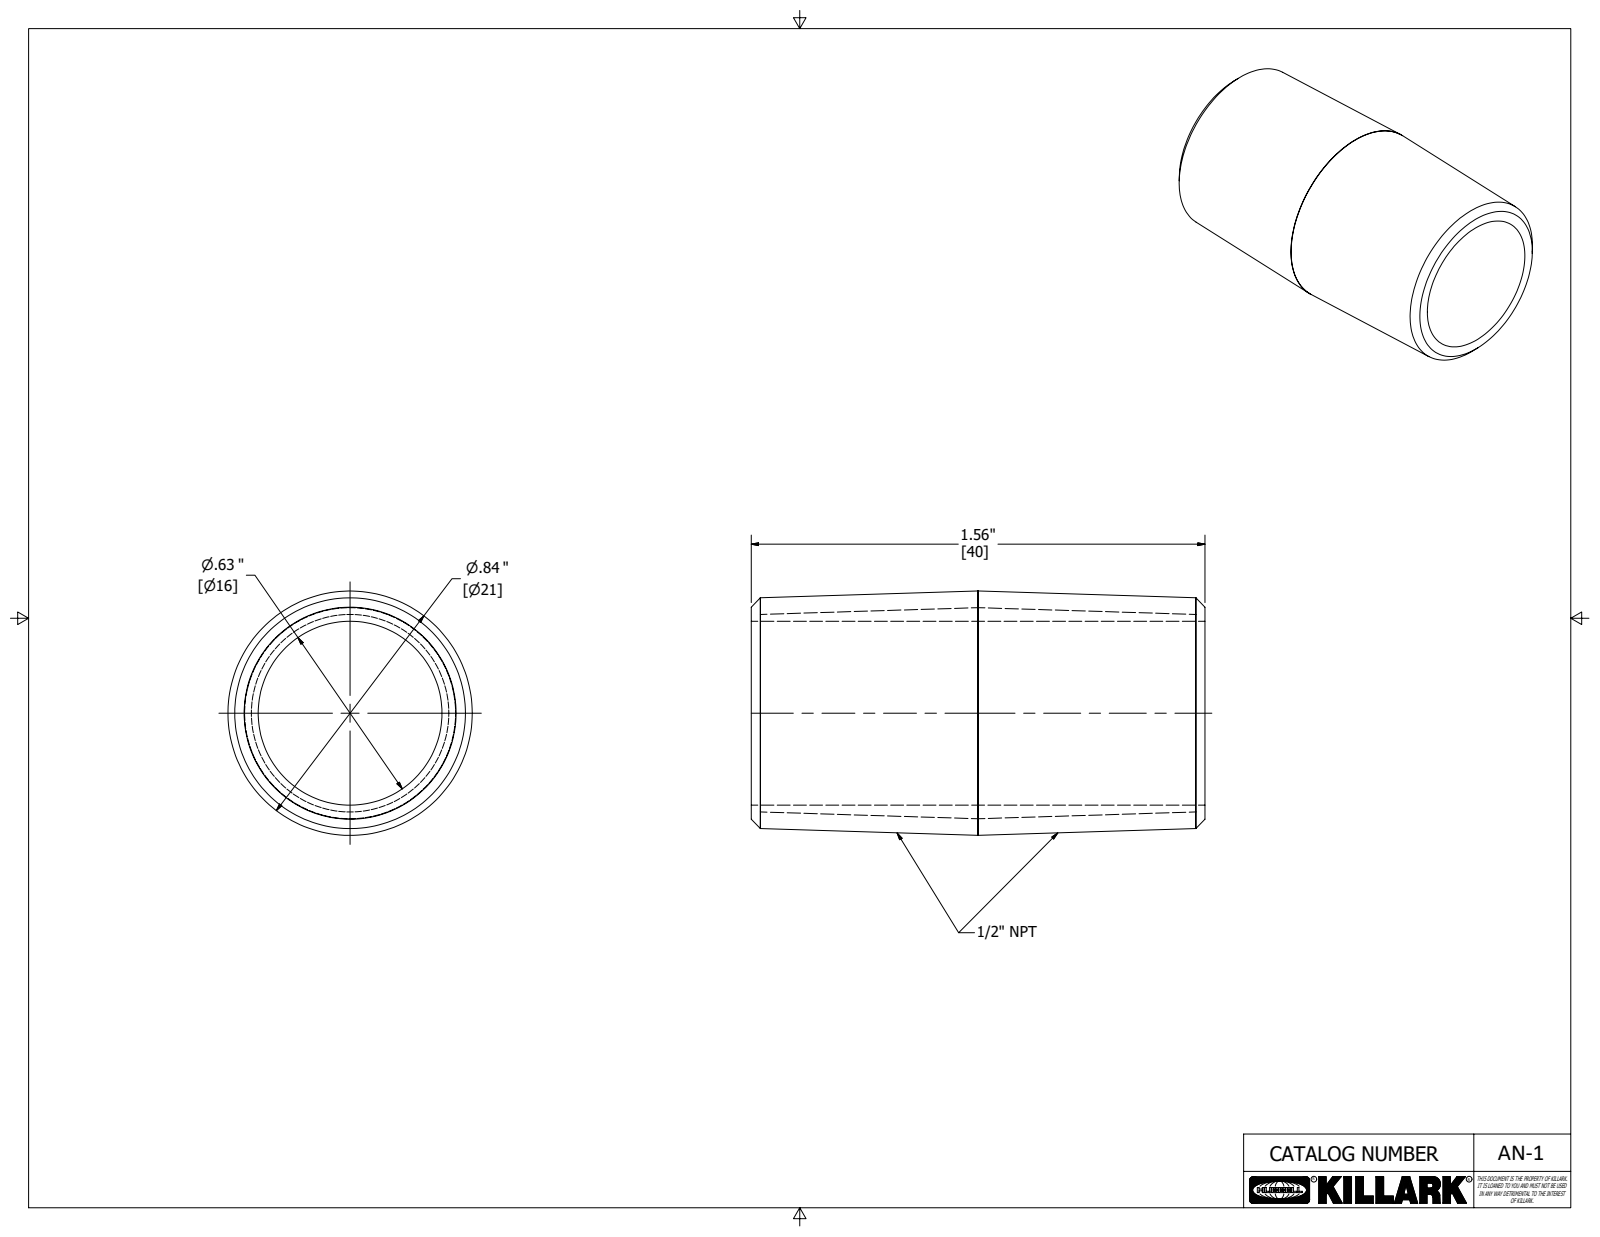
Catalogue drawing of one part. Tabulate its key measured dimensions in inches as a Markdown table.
| quantity | value |
| --- | --- |
| part name | 14077-1 |
| STEP written by | Autodesk Inventor 2020 (AUTOMOTIVE_DESIGN) |
| units | inches |
| bodies | 1 solid, 8 faces (2 planar, 2 cylindrical, 4 other) |
| overall size | 1.56 × 0.84 × 0.84 |
| volume | 0.324 in³ |
| surface area | 7.363 in² |
| round holes (diameter × count) | 0.632 × 1 |
| round bosses / shafts (diameter × count) | 0.84 × 1 |
| main face-to-face distances | 1.56 |
